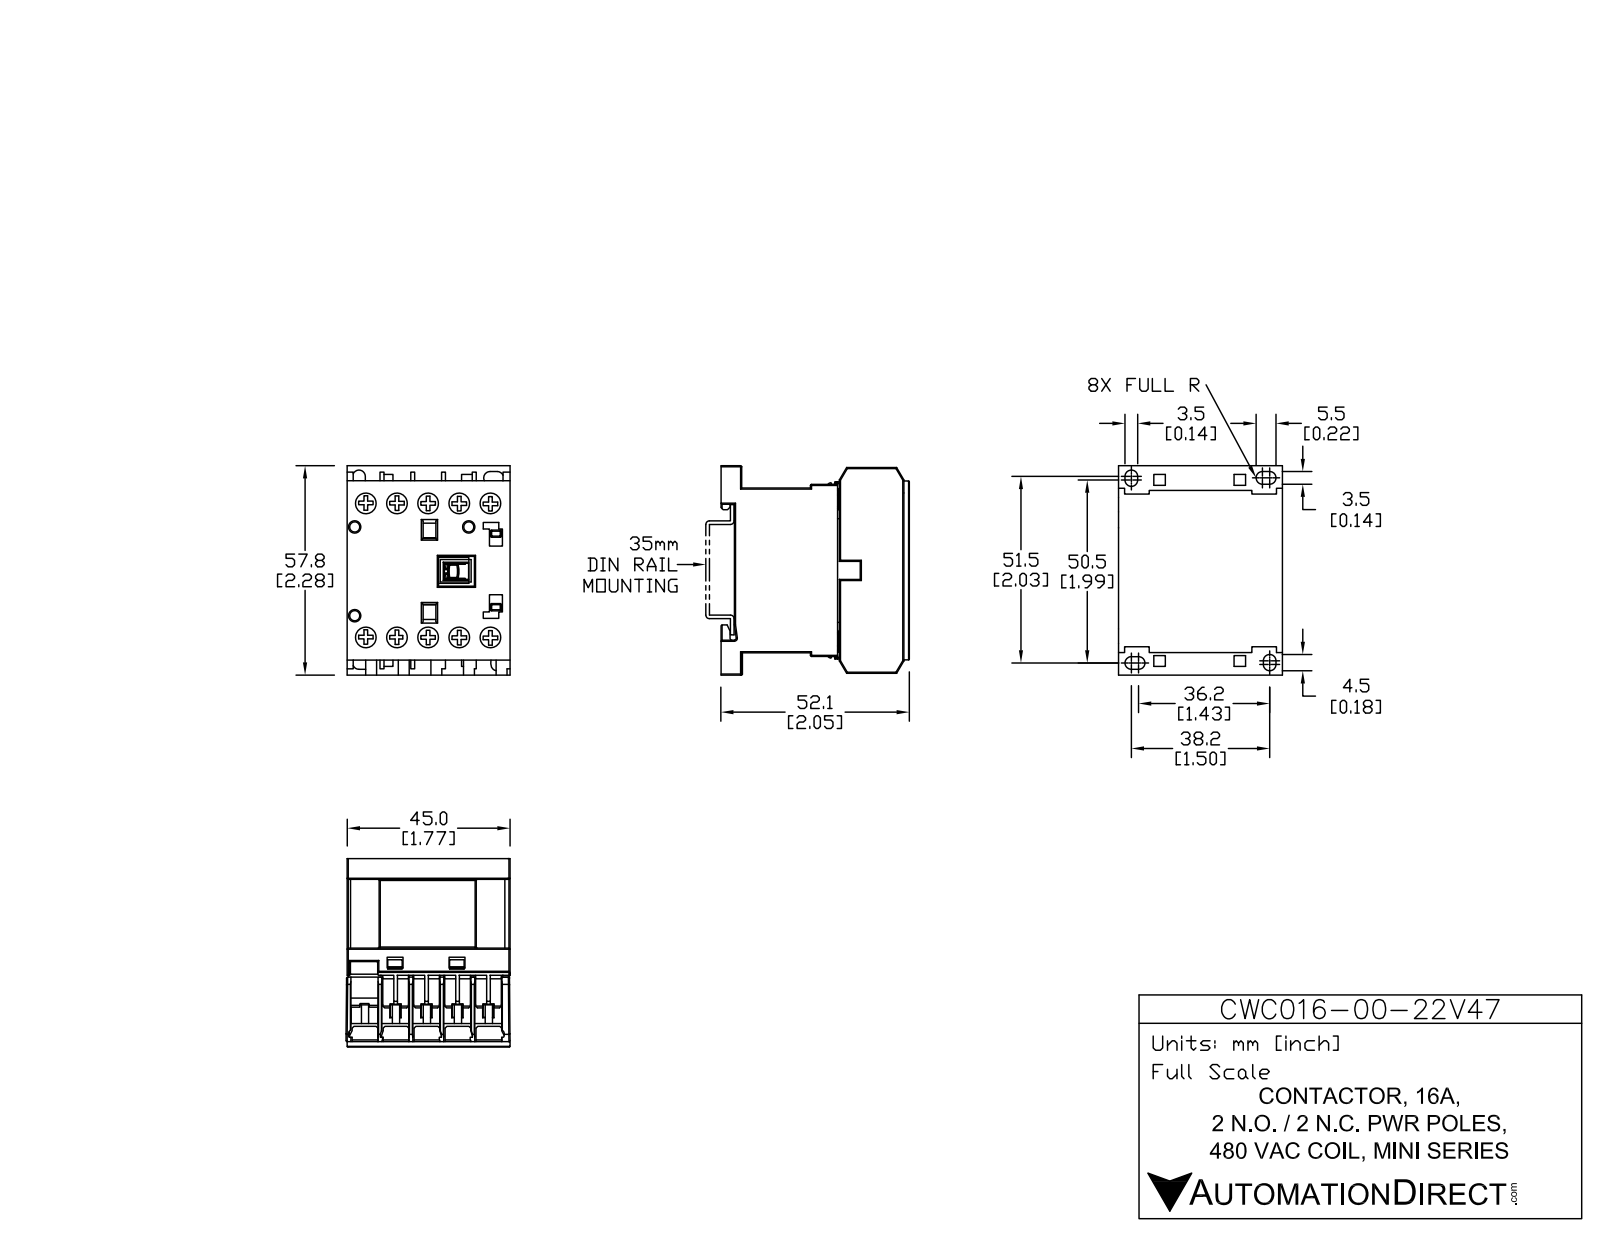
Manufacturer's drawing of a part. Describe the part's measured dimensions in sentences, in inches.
The part is named "CWC16-00-22V47". Its 3-D file was written by "SolidWorks 2013 (AUTOMOTIVE_DESIGN)". It is 15 solids with 535 faces: 445 planar, 90 cylindrical and 0 other. Overall it measures 2.285 by 2.052 by 1.801 inches. Its volume is 5.927 cubic inches and its surface area 47.18 square inches. Round holes: 10 of diameter 0.244, 3 of diameter 0.11. Round bosses or shafts: 10 of diameter 0.232. Partial cylindrical surfaces (rounded edges, fillets, slot ends): 20 of radius 0.012, 6 of radius 0.068, 2 of radius 0.068, 1 of radius 0.013, 1 of radius 0.017, 1 of radius 0.022. The main face-to-face distances are 0.325, 1.791, 0.049, 0.65, 0.374, 0.217, 0.699, 0.202, 0.419, 0.276. The hole center spacings are 0.337, 1.494, 0.673, 1.603, 1.455, 1.01, 1.771, 0.272.
